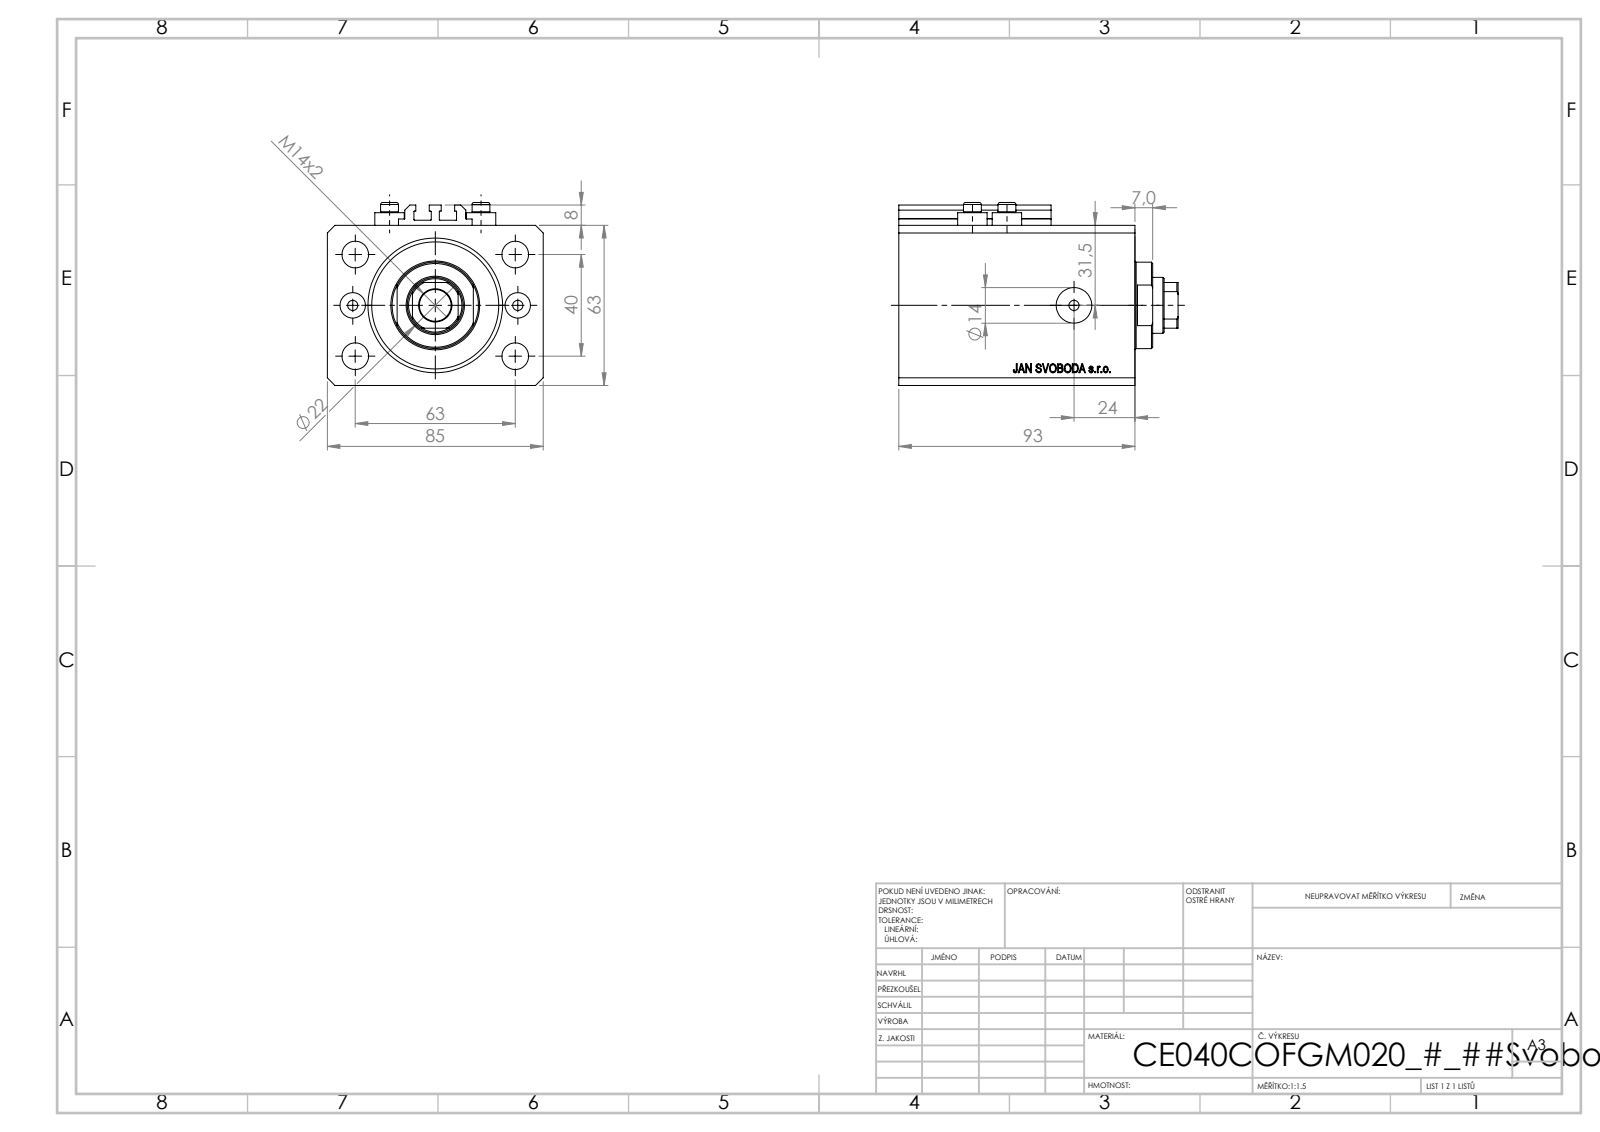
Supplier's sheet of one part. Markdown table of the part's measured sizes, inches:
| quantity | value |
| --- | --- |
| part name | V250CE_C_Body; V250CE_C_VCP; ALLEN BOLT V250CE; V250CE_VC_C |
| STEP written by | SolidWorks 2019 (CONFIG_CONTROL_DESIGN) |
| units | inches |
| bodies | 8 solids, 1034 faces (504 planar, 86 cylindrical, 444 other) |
| overall size | 4.331 × 3.346 × 2.835 |
| volume | 28.08 in³ |
| surface area | 142.9 in² |
| round holes (diameter × count) | 0.157 × 8, 0.413 × 4, 0.394 × 2, 0.551 × 2, 0.492 × 1, 0.866 × 1, 1.575 × 1, 2.087 × 1 |
| round bosses / shafts (diameter × count) | 0.457 × 4, 0.276 × 4, 1.339 × 1 |
| partial cylindrical surfaces (radius × count) | 0.008 × 10, 0.413 × 1 |
| main face-to-face distances | 2.48, 3.346, 3.661, 0.669, 2.992, 0.449, 2.543, 3.213, 0.118, 0.394 |
| hole center spacings | 0.788, 1.469, 2.64, 0.535, 1.28, 1.417, 1.515, 1.575 |
